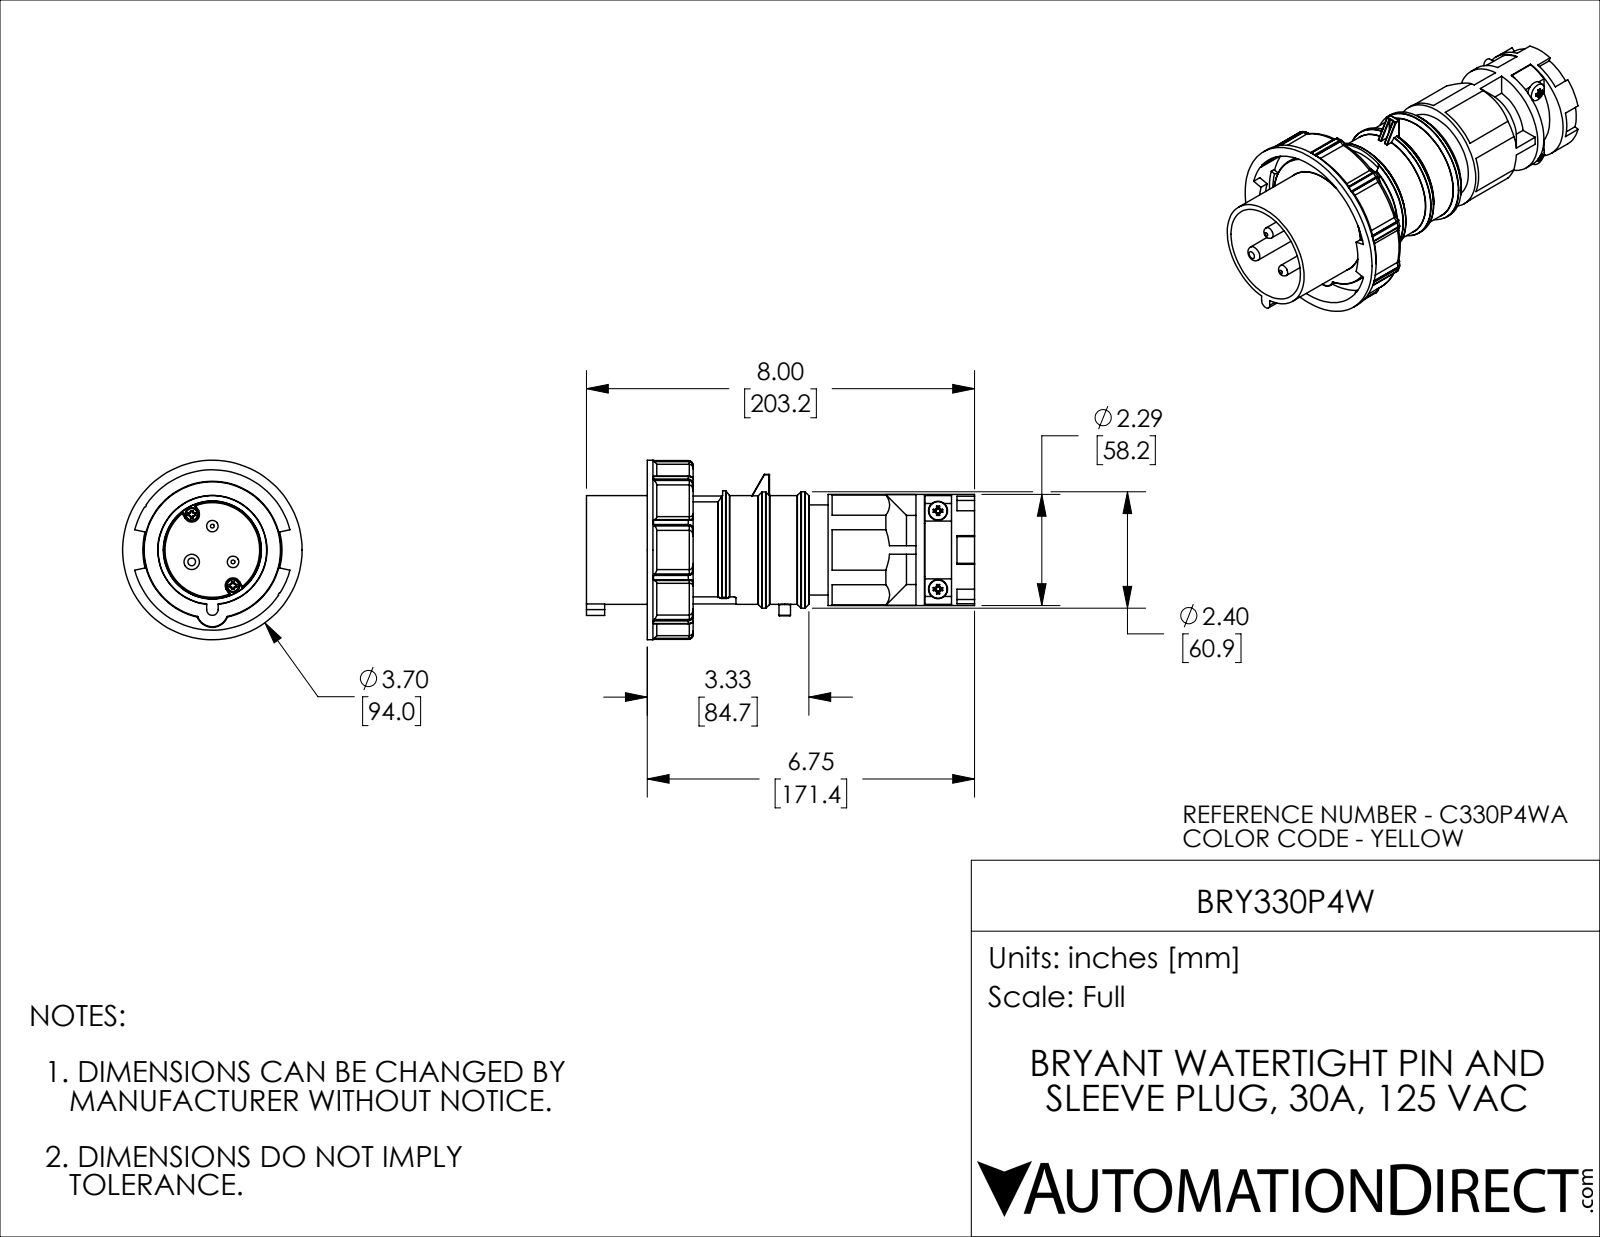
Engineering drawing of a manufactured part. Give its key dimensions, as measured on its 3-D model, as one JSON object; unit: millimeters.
{"part_name": "BRY330P4W", "step_written_by": "SolidWorks 2021 (CONFIG_CONTROL_DESIGN)", "units": "millimeters", "bodies": {"solids": 6, "faces": 804, "planar": 237, "cylindrical": 276, "other": 291}, "overall_size": [203.23, 94, 94], "volume_mm3": 402251, "surface_area_mm2": 100314, "round_holes": [[5, 2], [3.1, 1], [29.5, 1], [49.04, 1], [55.6, 1], [56.6, 1], [69.6, 1], [84, 1]], "round_bosses_or_shafts": [[6, 3], [94, 1], [72, 1], [66.6, 1], [62, 1], [61, 1], [58.2, 1], [57, 1]], "partial_cylinders_radius": [[0.5, 28], [2.5, 20], [0.25, 13], [1, 7], [3, 3], [0.3, 2], [1.2, 2], [3.55, 2]], "face_to_face_distances": [4.5, 70.73, 64.7, 135.43, 18.7, 10, 143.73, 79.03, 8.3, 54.2], "hole_center_spacings": [41]}
